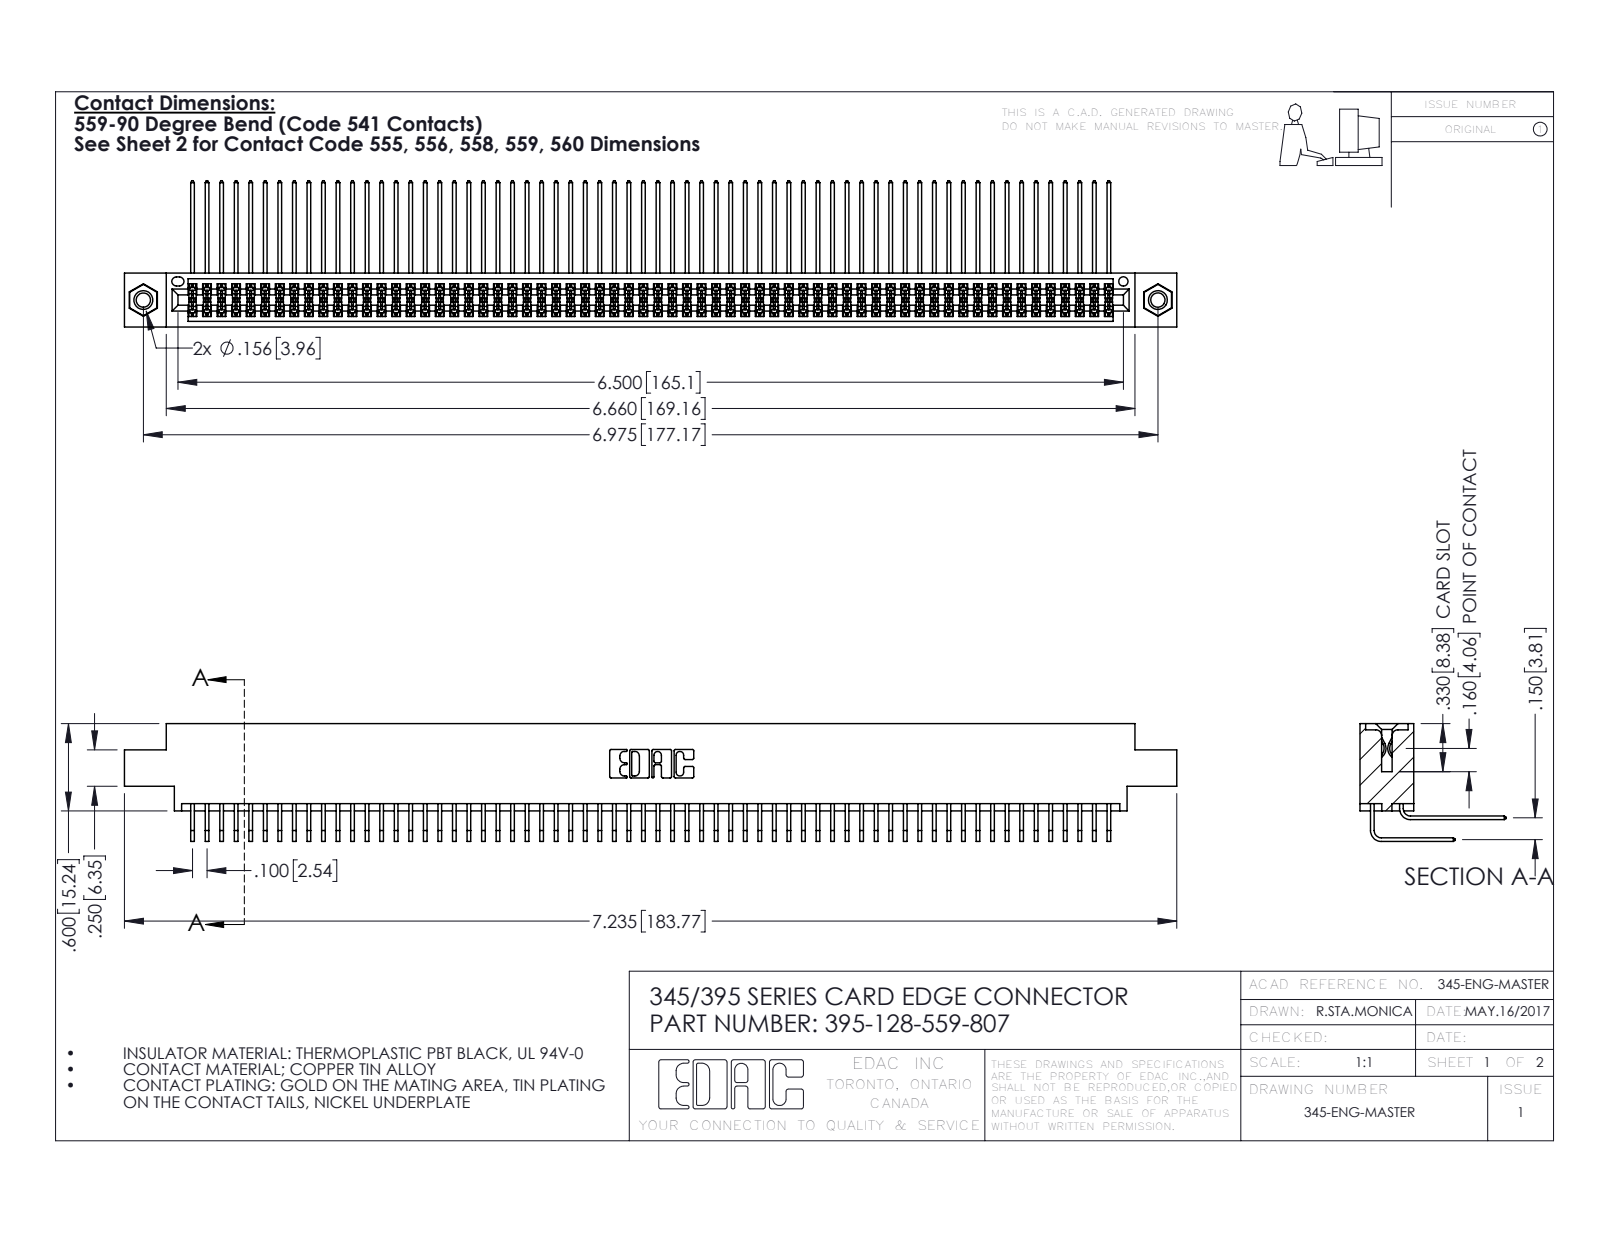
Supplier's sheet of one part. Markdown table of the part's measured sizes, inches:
| quantity | value |
| --- | --- |
| part name | 395-128-559-807; 345-292-001_559 Tail - 2; 345 Part_0.170 Offset - 0.156 Dia-TI; 345-292-001_558 559 Tail - 1 (+1 more) |
| STEP written by | SolidWorks 2016 (CONFIG_CONTROL_DESIGN) |
| units | inches |
| bodies | 131 solids, 6846 faces (4596 planar, 2234 cylindrical, 16 other) |
| overall size | 7.235 × 1.005 × 0.809 |
| volume | 1.139 in³ |
| surface area | 49.08 in² |
| round holes (diameter × count) | 0.098 × 2, 0.125 × 2, 0.156 × 2, 0.064 × 1 |
| round bosses / shafts (diameter × count) | 0.155 × 2 |
| partial cylindrical surfaces (radius × count) | 0.006 × 193, 0.01 × 22, 0.007 × 6, 0.031 × 6, 0.026 × 3, 0.014 × 2, 0.019 × 2, 0.022 × 2 |
| main face-to-face distances | 0.072, 0.298, 0.37, 0.2, 0.098, 0.272, 0.025, 0.225, 0.175, 0.15 |
| hole center spacings | 0.27, 6.739, 6.975 |
